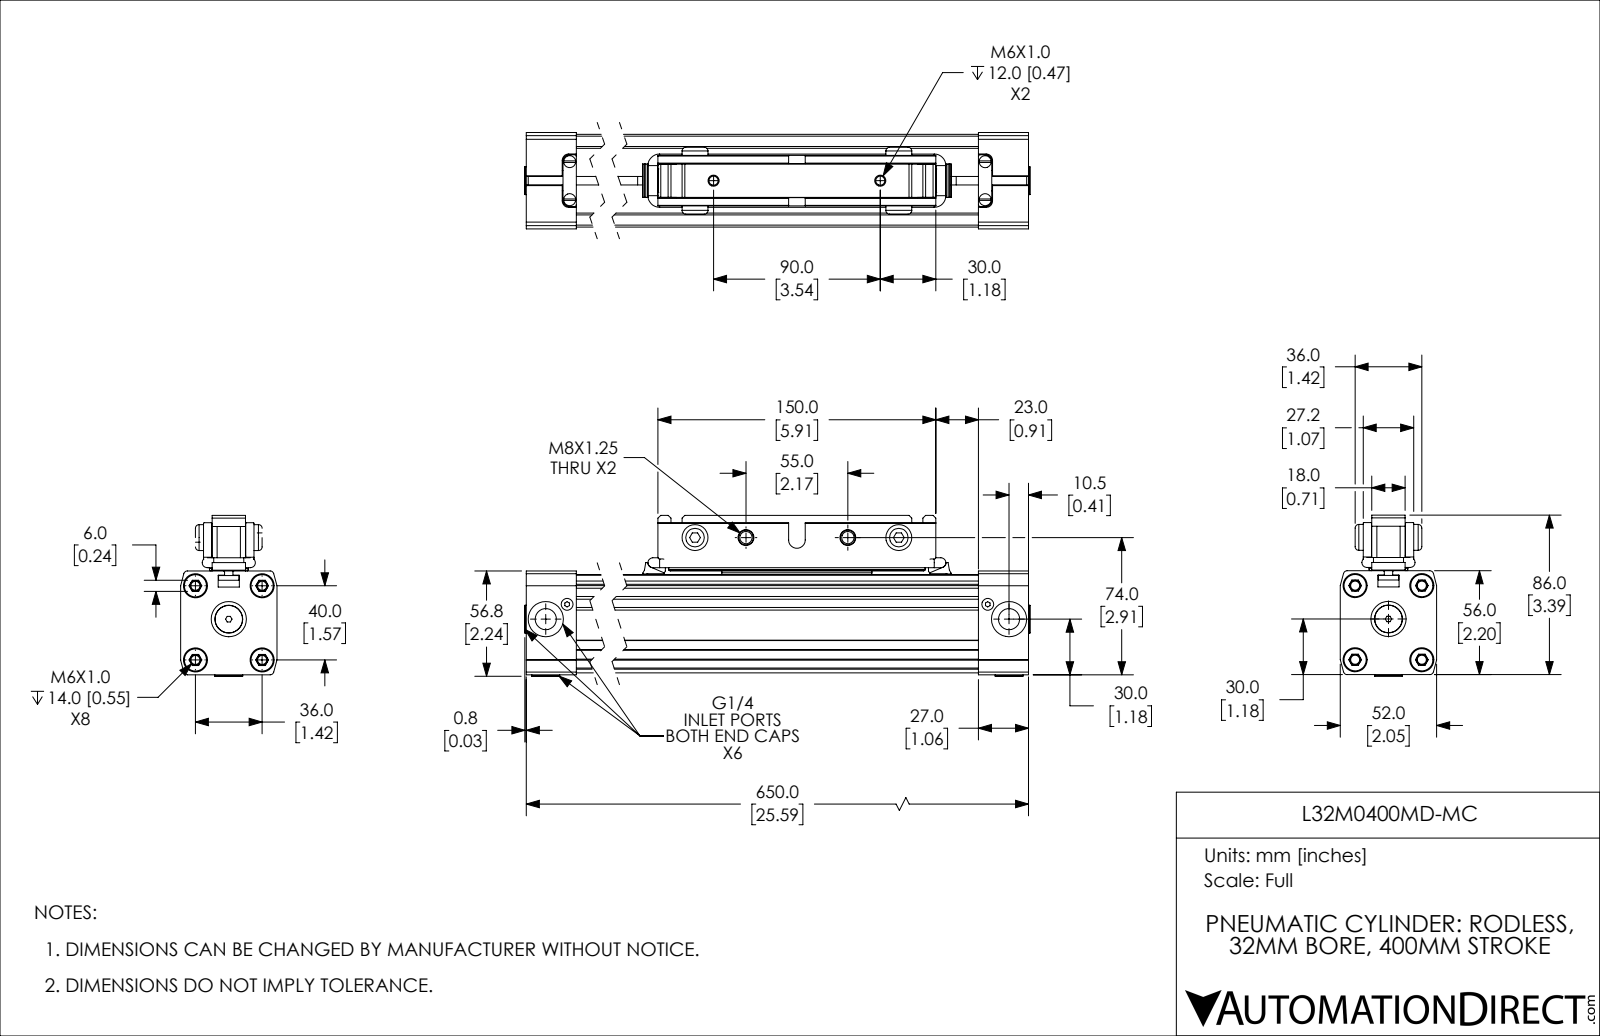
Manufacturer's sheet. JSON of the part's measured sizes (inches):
{"part_name": "L32M0400MD-MC_PISTON; L32M0400MD-MC; L32M0400MD-MC_BODY", "step_written_by": "SolidWorks 2019 (CONFIG_CONTROL_DESIGN)", "units": "inches", "bodies": {"solids": 13, "faces": 822, "planar": 433, "cylindrical": 273, "other": 116}, "overall_size": [25.652, 3.417, 2.047], "volume_in3": 79.32, "surface_area_in2": 494.4, "round_holes": [[0.194, 6], [0.451, 5], [0.748, 5], [0.256, 4], [0.262, 4], [0.339, 4], [0.512, 4], [0.252, 2], [1.264, 1]], "round_bosses_or_shafts": [[0.472, 4], [0.21, 4], [0.591, 3], [0.383, 3], [0.323, 3], [0.551, 2], [1.26, 1], [1.252, 1]], "partial_cylinders_radius": [[0.039, 22], [0.079, 18], [0.138, 8], [0.012, 4], [0.02, 4], [0.024, 4], [0.157, 4], [0.006, 2]], "face_to_face_distances": [2.087, 1.969, 0.201, 0.445, 0.181, 1.072, 0.894, 1.075, 0.551, 0.449], "hole_center_spacings": [0.649, 24.259, 0.552, 0.807, 0.935, 1.002, 1.083, 1.119]}
